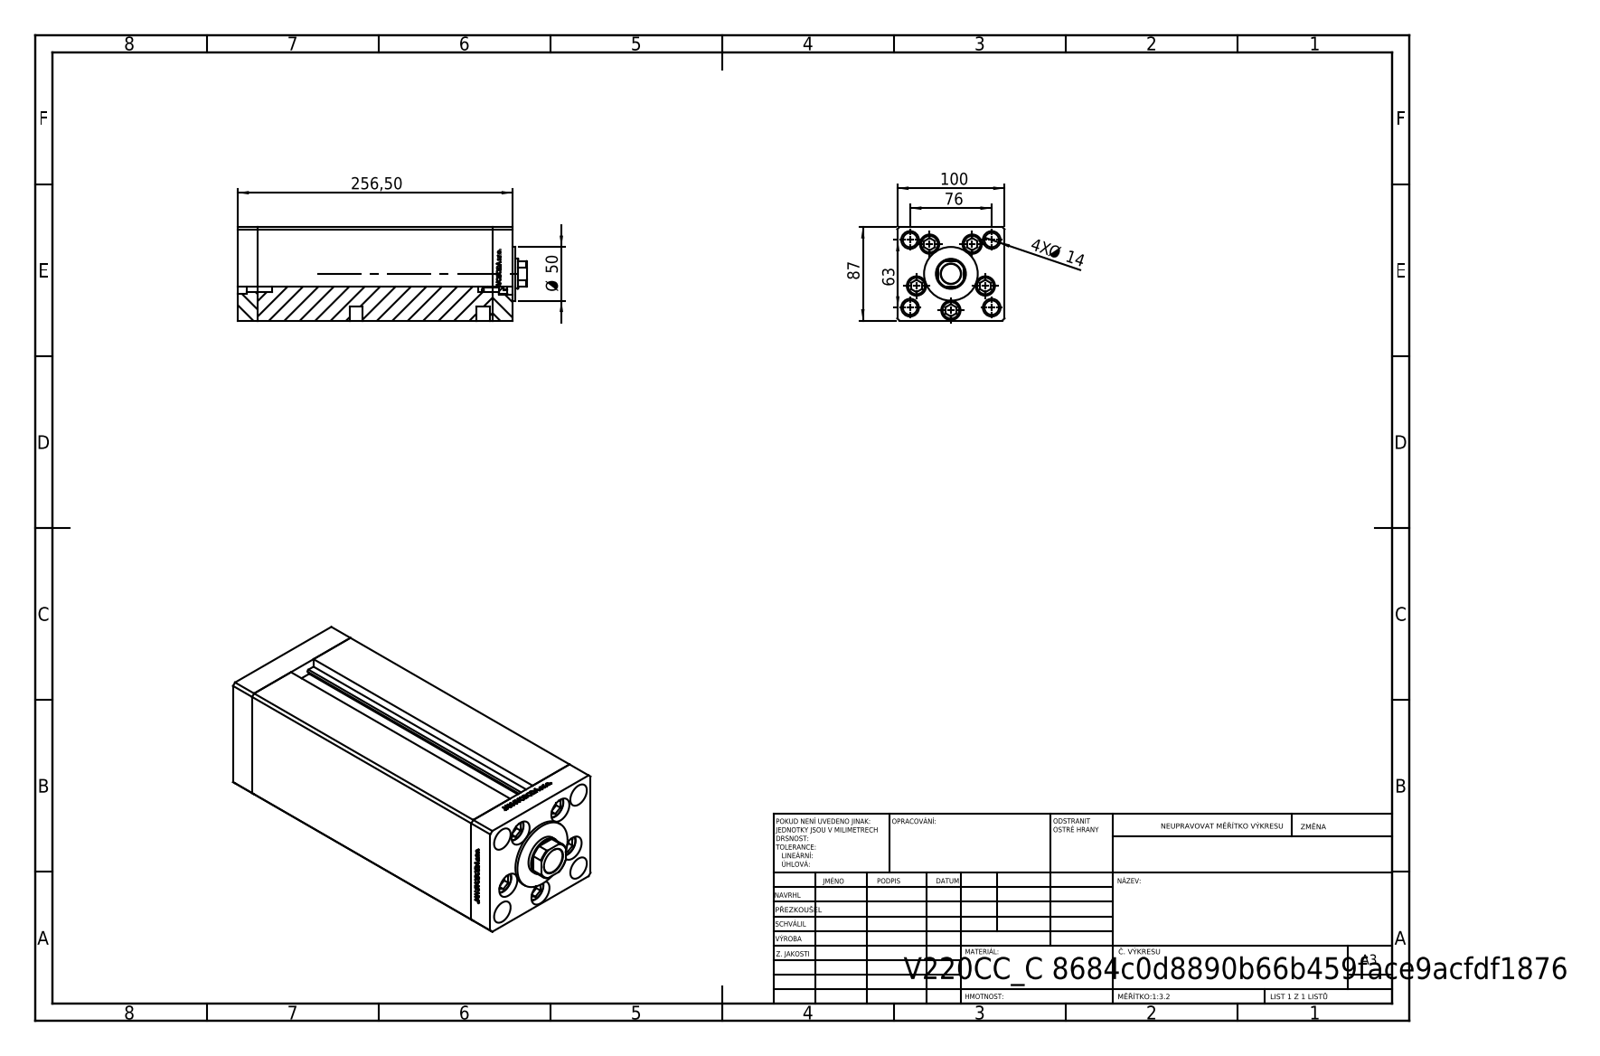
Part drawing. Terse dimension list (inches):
name: V220C_VC_C; ALLEN BOLT; V220C FRONT; V220C_C MIDDLE (+1 more)
written by: SolidWorks 2019 (CONFIG_CONTROL_DESIGN)
unit: in
bodies: 13 solids, 1186 faces (548 planar, 176 cylindrical, 462 other)
size: 10.61 × 3.937 × 3.425
volume: 111.1 in³; area: 433.2 in²
holes: 9× ⌀0.531, 5× ⌀0.709, 4× ⌀0.079, 4× ⌀0.472, 4× ⌀0.518, 4× ⌀0.65, 1× ⌀0.669, 1× ⌀0.728, 1× ⌀1.102
bosses: 5× ⌀0.315, 4× ⌀0.669, 1× ⌀1.969
rounds: 2× R0.037, 1× R0.531
face distances: 3.937, 3.425, 0.748, 8.602, 9.35, 1.348, 10.098, 8.75, 8.002, 0.6
hole spacings: 1.339, 1.943, 0.732, 0.828, 1.499, 1.546, 1.607, 1.702
